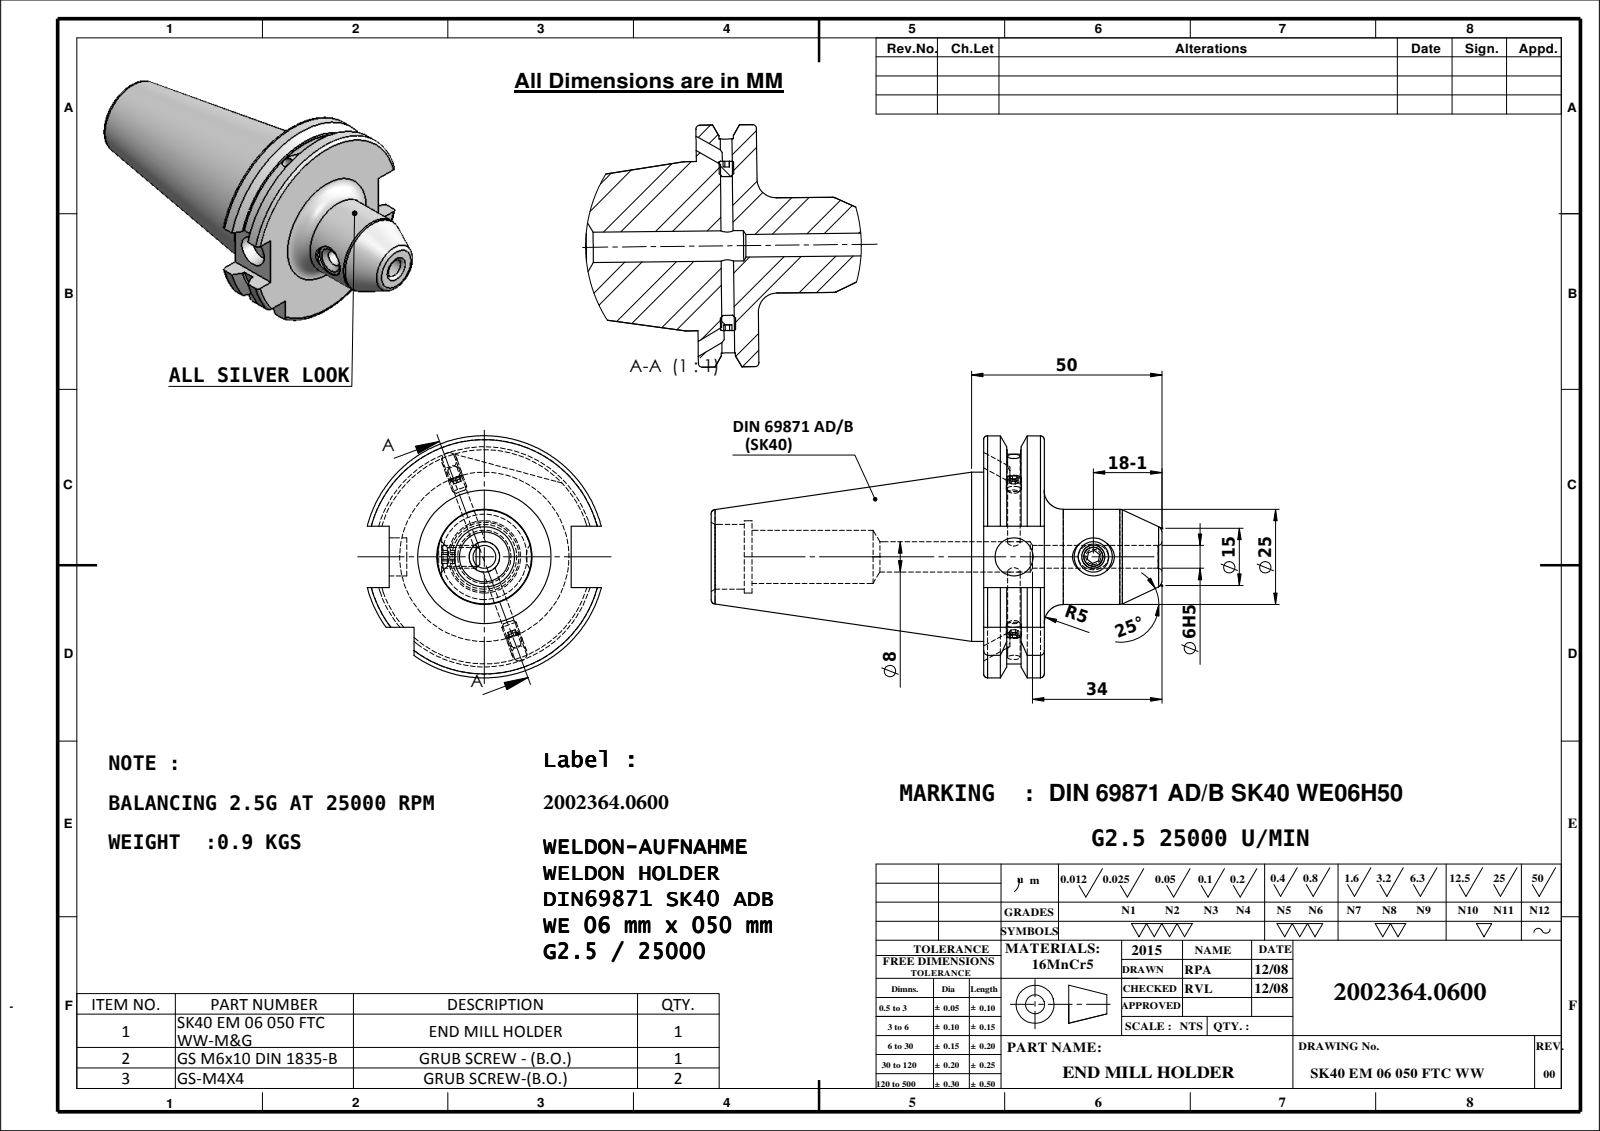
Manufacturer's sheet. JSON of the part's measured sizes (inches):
{"part_name": "SK40 EM 06 050 FTC WW-M&G; 91406-WE77 06050; M6X10_DIN 913 - M6 x 10-N; M4X4_DIN 913 - M4 x 4-N", "step_written_by": "SolidWorks 2009 (CONFIG_CONTROL_DESIGN)", "units": "inches", "bodies": {"solids": 4, "faces": 157, "planar": 56, "cylindrical": 42, "other": 59}, "overall_size": [4.661, 2.502, 2.42], "volume_in3": 7.069, "surface_area_in2": 36.61, "round_holes": [[0.394, 2], [0.13, 1], [0.197, 1], [0.236, 1], [0.315, 1], [0.551, 1], [0.669, 1], [0.748, 1]], "round_bosses_or_shafts": [[0.157, 2], [1.75, 1], [0.984, 1], [0.236, 1]], "partial_cylinders_radius": [[1.107, 1], [1.251, 1]], "face_to_face_distances": [0.626, 0.634, 1.882, 2.819, 3.445, 0.421, 2.398, 3.024, 3.056, 2.635], "hole_center_spacings": [0.821]}
